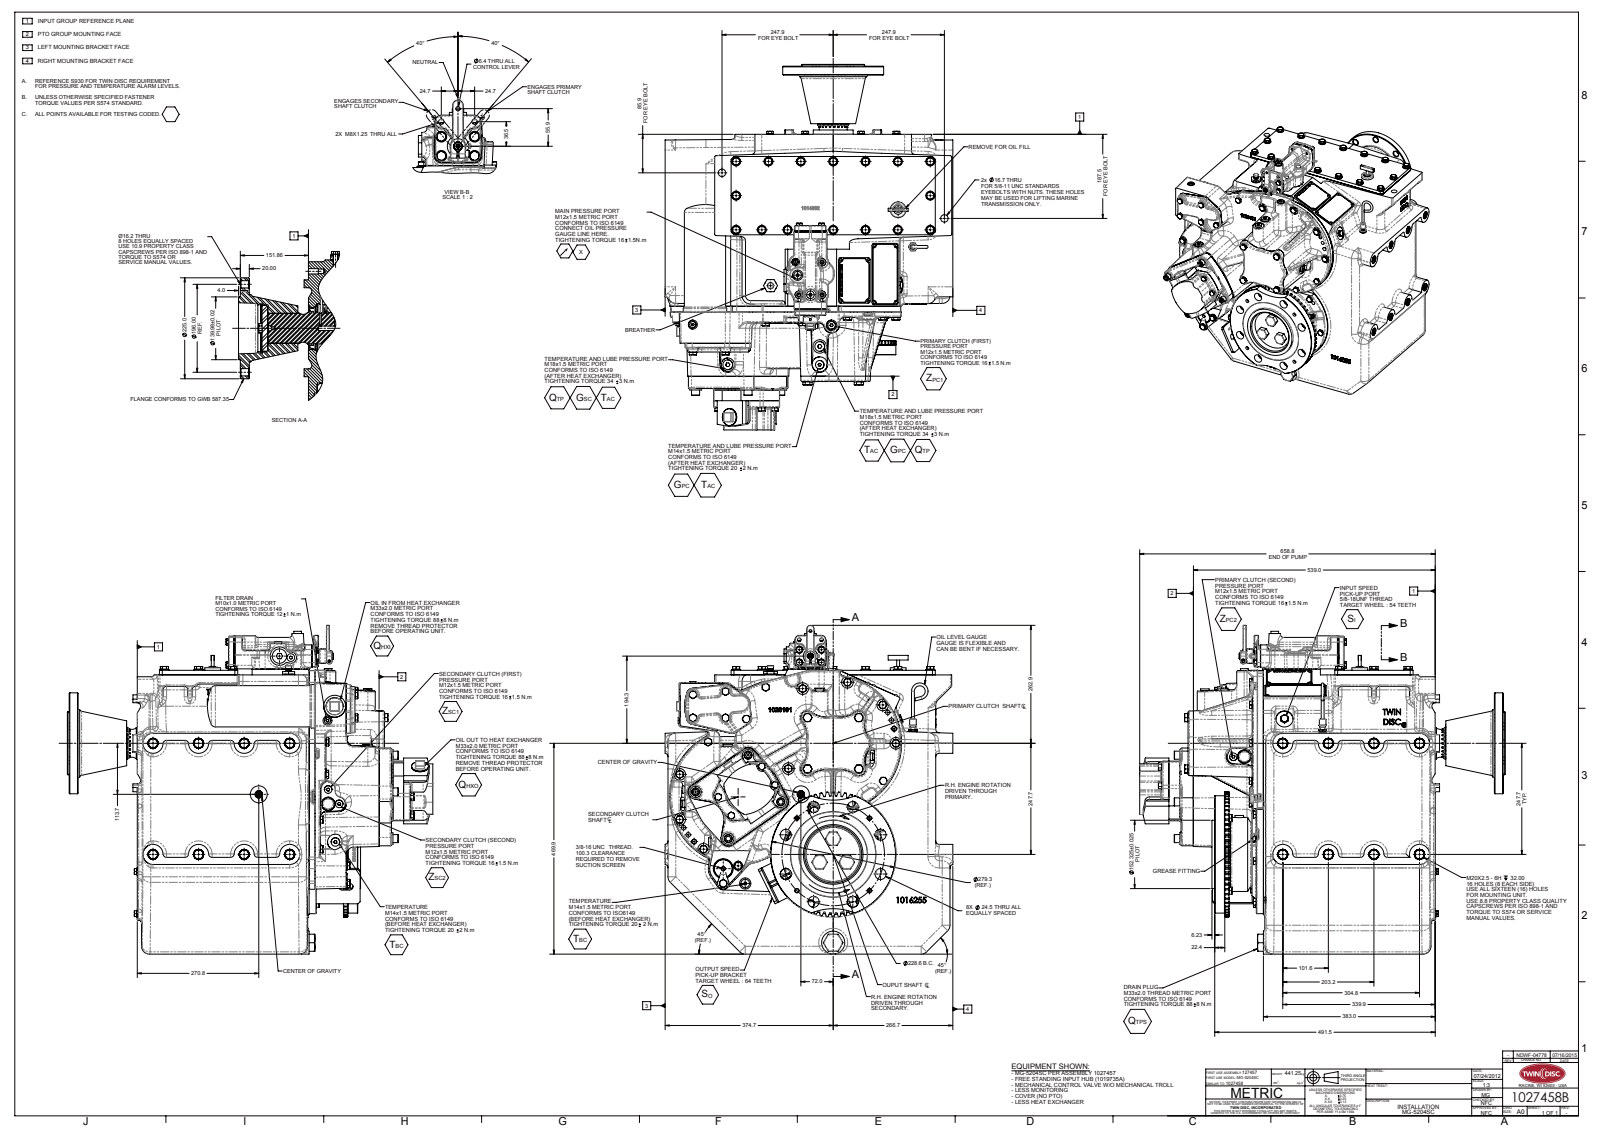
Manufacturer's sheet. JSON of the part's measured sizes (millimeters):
{"part_name": "1027458B", "step_written_by": "SolidWorks 2010 (AUTOMOTIVE_DESIGN)", "units": "millimeters", "bodies": {"solids": 0, "faces": 3899, "planar": 1144, "cylindrical": 1166, "other": 1589}, "overall_size": [814.69, 732.83, 641.35], "round_holes": [[12, 12], [16.2, 8], [22.82, 8], [24.5, 8], [10, 7], [6.8, 4], [16.5, 4], [8, 2], [10, 2], [11, 2], [16.67, 2], [20, 2]], "round_bosses_or_shafts": [[20, 17], [16.8, 7], [18, 6], [15.32, 4], [13, 4], [18.9, 3], [6.35, 3], [38.1, 2]], "partial_cylinders_radius": [[46.33, 87], [7.87, 75], [3, 68], [3.05, 53], [12, 49], [1.52, 37], [17.53, 32], [6.4, 26]], "face_to_face_distances": [0.39, 13.49, 13.1, 396.52, 396.13, 383.03, 596.9, 632.59, 622.3, 10.29], "hole_center_spacings": [101.6, 203.2, 247.65, 267.68, 320.34, 49.48, 79.38, 127]}
